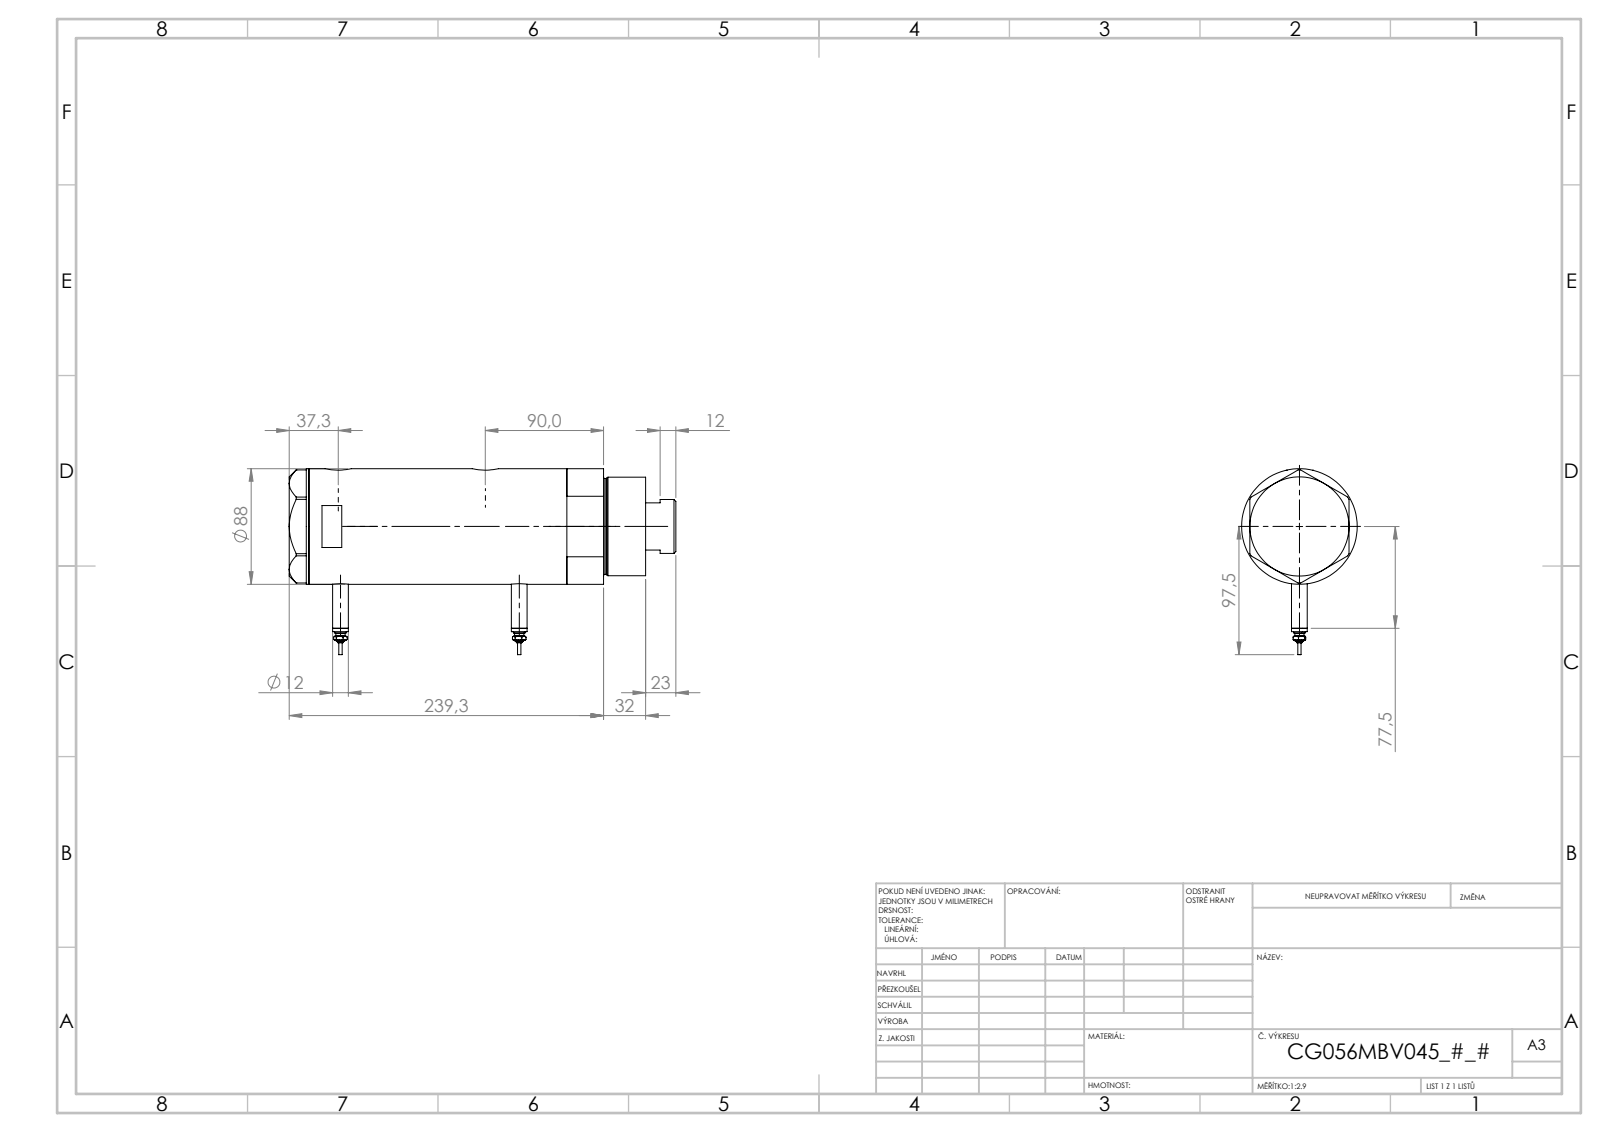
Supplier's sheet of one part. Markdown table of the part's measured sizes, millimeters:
| quantity | value |
| --- | --- |
| part name | V270CG_MIDDLE; Switch; V270CG_VC; V270CG_BACK (+1 more) |
| STEP written by | SolidWorks 2019 (CONFIG_CONTROL_DESIGN) |
| units | millimeters |
| bodies | 6 solids, 213 faces (80 planar, 69 cylindrical, 64 other) |
| overall size | 294.3 × 141.5 × 88 |
| volume | 1 547 000 mm³ |
| surface area | 224 809 mm² |
| round holes (diameter × count) | 12.5 × 2, 13.16 × 2, 20 × 2, 14.5 × 1, 42 × 1, 43.5 × 1, 56 × 1, 60 × 1, 80 × 1 |
| round bosses / shafts (diameter × count) | 12 × 2, 9 × 2, 7 × 2, 4.5 × 2, 2.5 × 2, 88 × 1, 75 × 1, 73 × 1 |
| main face-to-face distances | 134.4, 26, 108.4, 15, 41, 149.4, 256.3, 271.3, 230.3, 121.9 |
| hole center spacings | 1.7, 25.8, 110.3, 112, 136.1, 137.8 |
